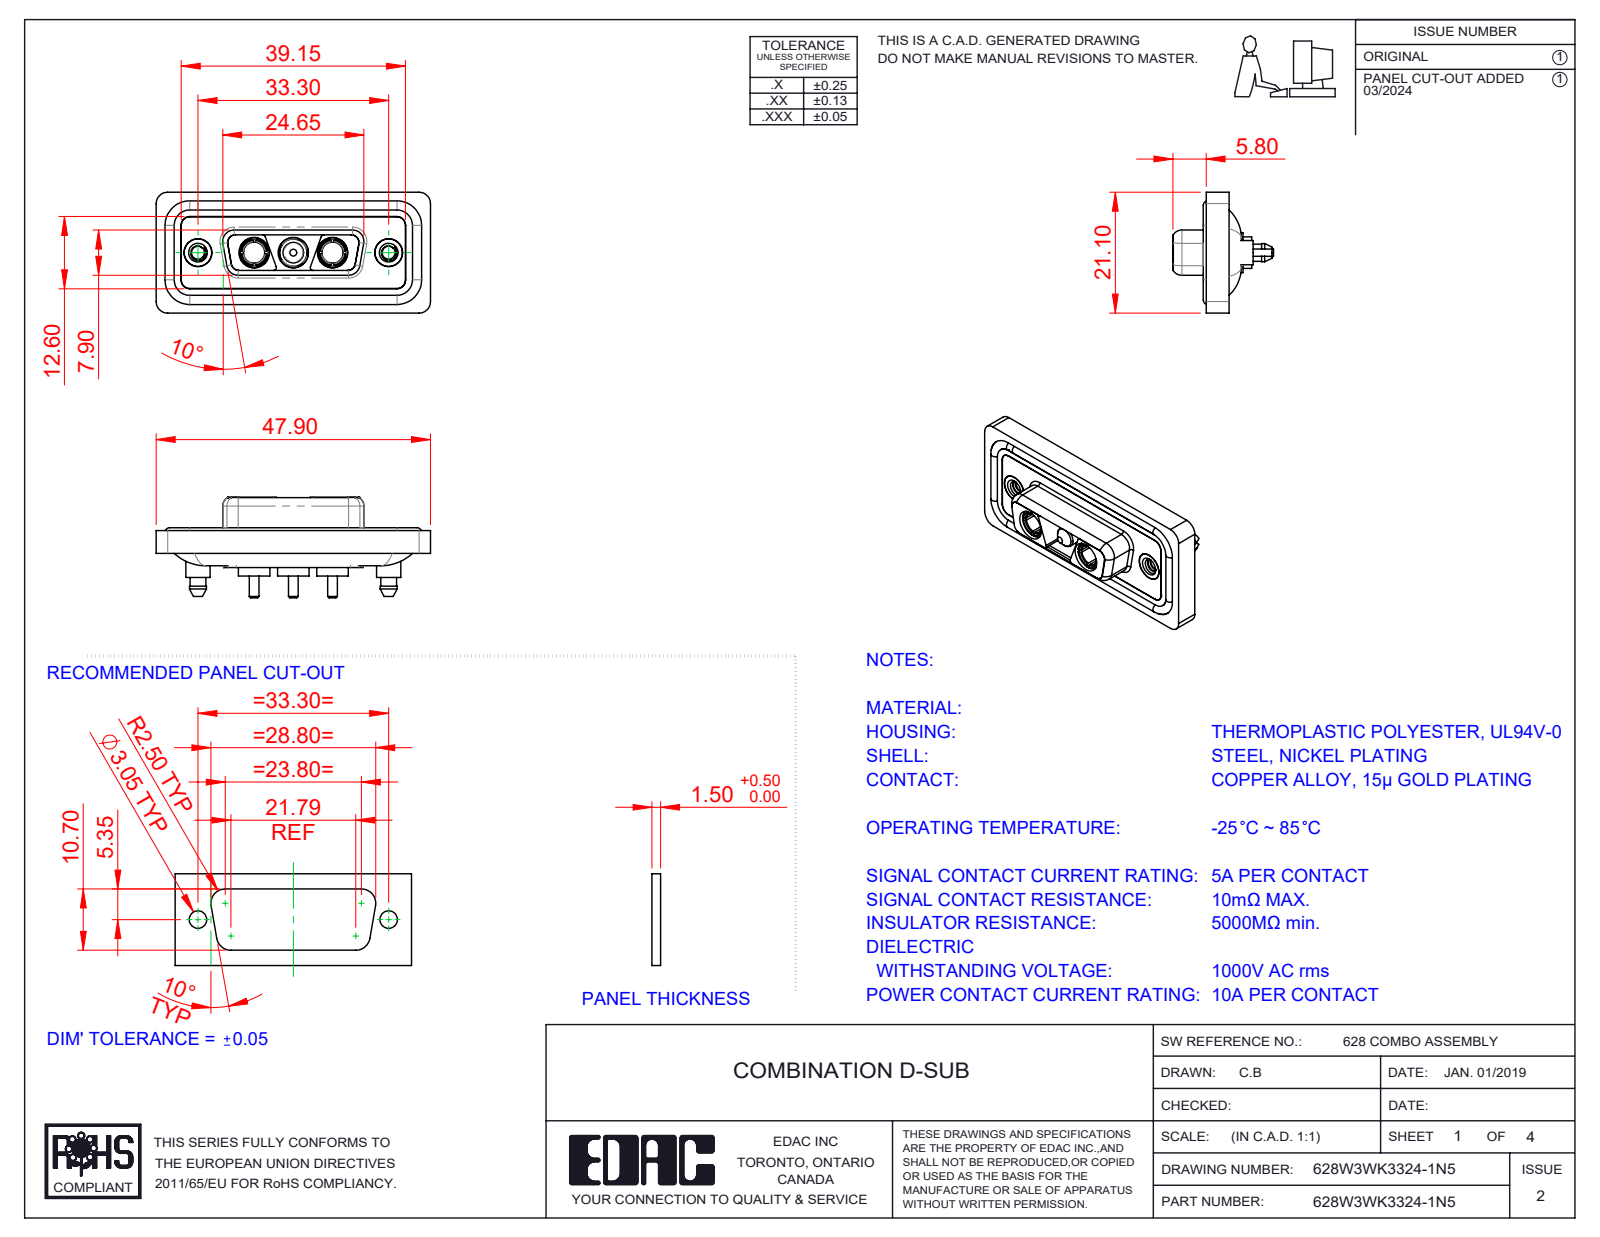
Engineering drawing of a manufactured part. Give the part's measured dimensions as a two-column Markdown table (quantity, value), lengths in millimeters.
| quantity | value |
| --- | --- |
| part name | 628Combo Shell Front_15 Contacts; Power Socket_10A S; 628W3WK3324-1N5; Power Pin_10A S (+4 more) |
| STEP written by | SolidWorks 2023 (CONFIG_CONTROL_DESIGN) |
| units | millimeters |
| bodies | 13 solids, 633 faces (194 planar, 290 cylindrical, 149 other) |
| overall size | 47.9 × 21.1 × 17.55 |
| volume | 5 968 mm³ |
| surface area | 9 800 mm² |
| round holes (diameter × count) | 4.85 × 5, 5.3 × 3, 2.26 × 2, 3.7 × 2, 4 × 2, 4.05 × 2, 5 × 2 |
| round bosses / shafts (diameter × count) | 1.6 × 4, 5.5 × 3, 5.2 × 3, 4.75 × 3, 3.75 × 3, 1.7 × 3, 5.4 × 2, 4.96 × 2 |
| partial cylindrical surfaces (radius × count) | 1.5 × 24, 2 × 20, 1.35 × 12, 1.6 × 10, 0.5 × 8, 0.25 × 4, 0.6 × 4, 0.65 × 4 |
| main face-to-face distances | 0.4, 1.6, 1.8, 0.5, 1.1, 2.9, 5.65, 7.05, 1.5, 5.35 |
| hole center spacings | 6.85, 9.8, 16.65, 23.5, 13.7, 33.3 |
